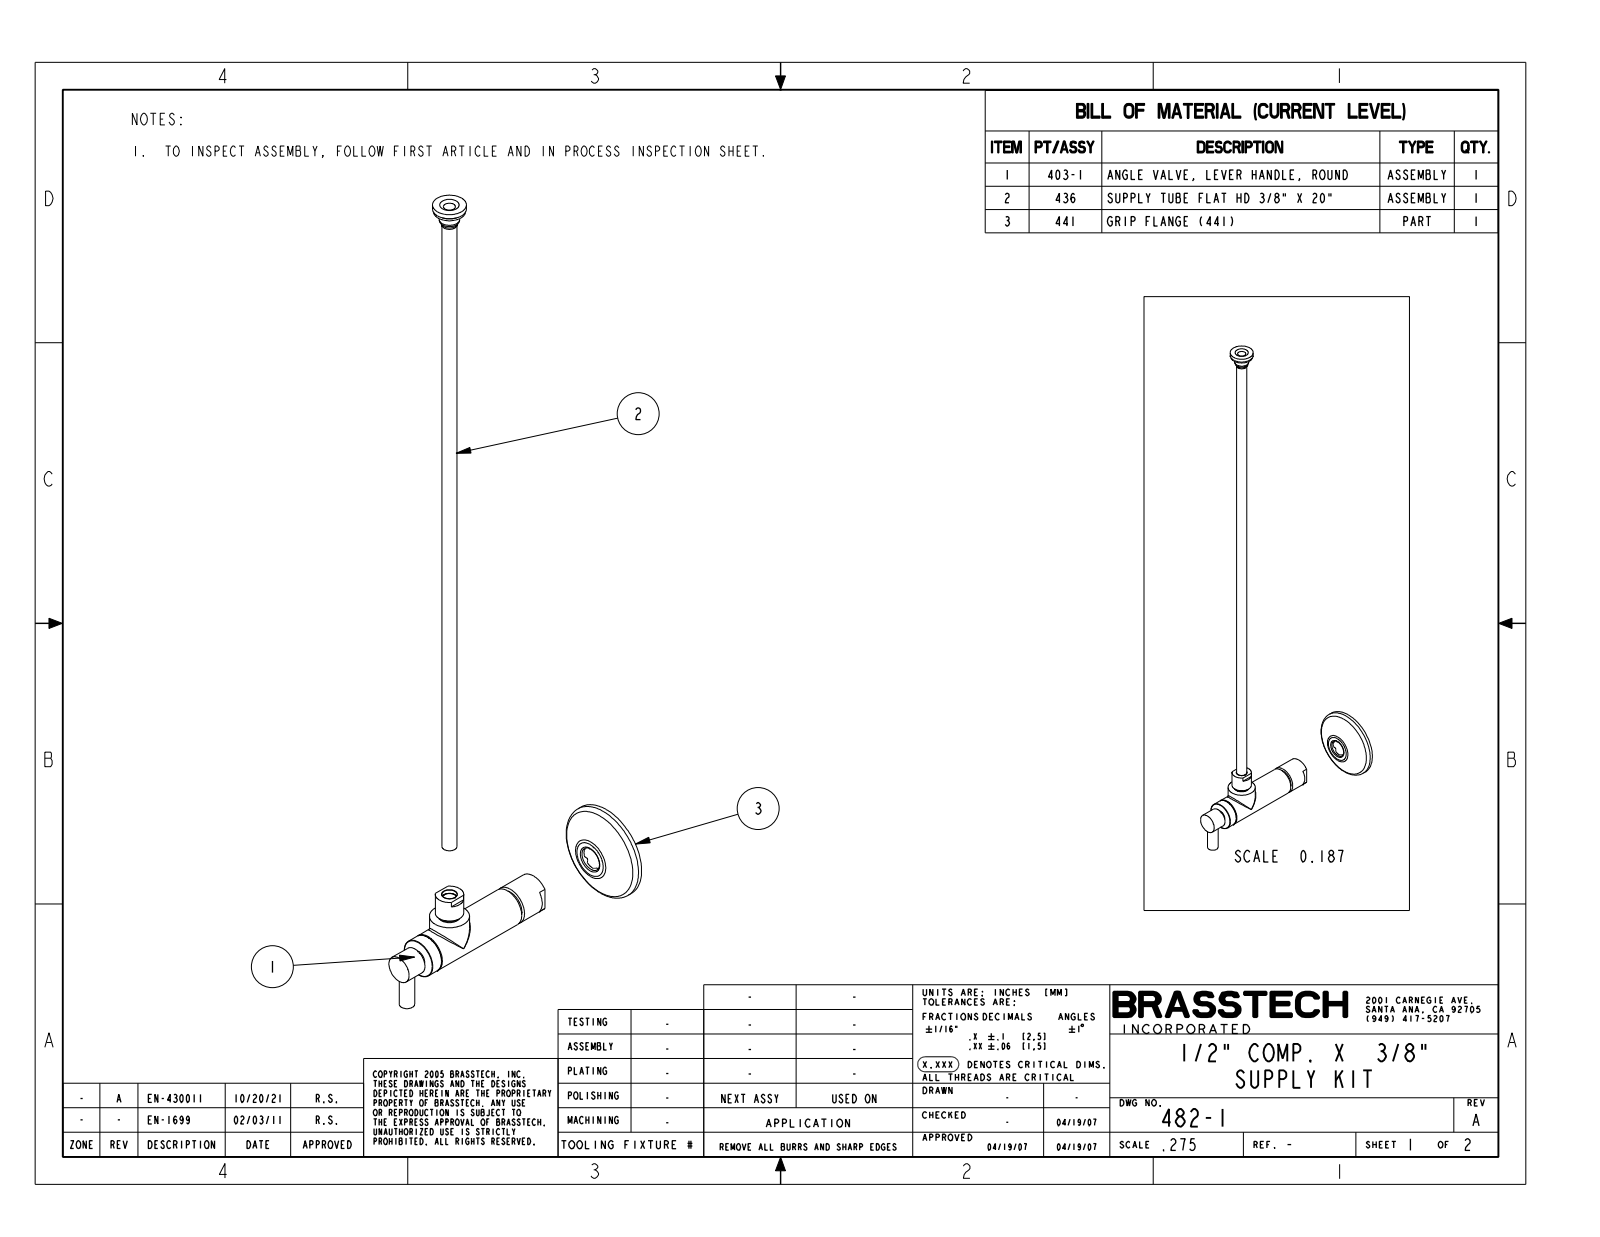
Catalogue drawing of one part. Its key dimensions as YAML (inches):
part_name: "482-1"
step_written_by: "CREO PARAMETRIC BY PTC INC, 2018500 (CONFIG_CONTROL_DESIGN)"
units: inches
bodies: {solids: 8, faces: 803, planar: 200, cylindrical: 383, other: 220}
overall_size: [21.575, 7.314, 2.5]
volume: 2.644
surface_area: 160.6
round_holes:
  - {diameter: 0.3, count: 2}
  - {diameter: 0.145, count: 1}
  - {diameter: 0.15, count: 1}
  - {diameter: 0.19, count: 1}
  - {diameter: 0.275, count: 1}
  - {diameter: 0.32, count: 1}
  - {diameter: 0.328, count: 1}
  - {diameter: 0.335, count: 1}
  - {diameter: 0.38, count: 1}
  - {diameter: 0.382, count: 1}
  - {diameter: 0.385, count: 1}
  - {diameter: 0.387, count: 1}
round_bosses_or_shafts:
  - {diameter: 1, count: 2}
  - {diameter: 0.885, count: 1}
  - {diameter: 0.845, count: 1}
  - {diameter: 0.819, count: 1}
  - {diameter: 0.8, count: 1}
  - {diameter: 0.776, count: 1}
  - {diameter: 0.717, count: 1}
  - {diameter: 0.71, count: 1}
partial_cylinders:
  - {radius: 0.03, count: 10}
  - {radius: 0.058, count: 5}
  - {radius: 0.005, count: 2}
  - {radius: 0.134, count: 1}
  - {radius: 0.199, count: 1}
face_to_face_distances: [4.064, 2.314, 1.75, 4.744, 2.43, 0.68, 0.814, 1.5, 3.25, 3.93]
hole_center_spacings: [0.043, 1.457, 1.5]
